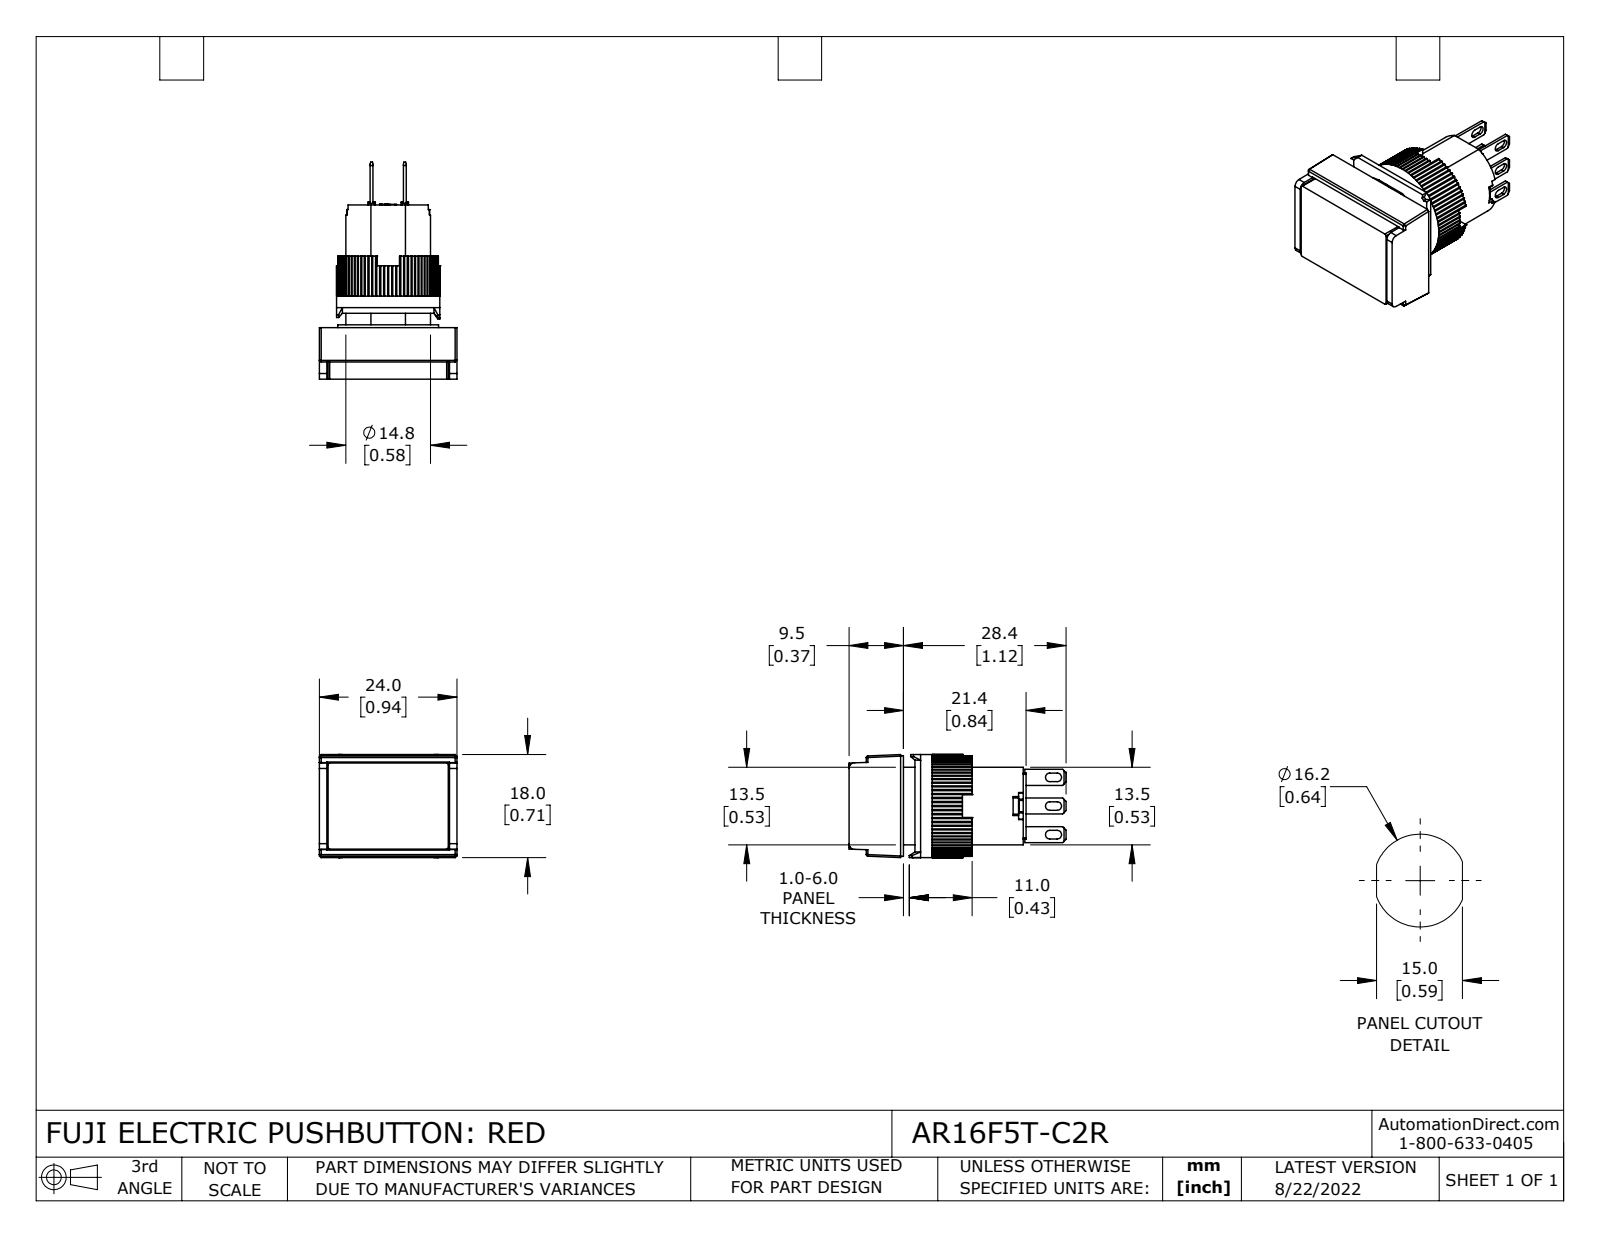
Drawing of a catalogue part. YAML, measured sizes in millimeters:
part_name: "AR16F5T-C2R"
step_written_by: "SolidWorks 2021 (CONFIG_CONTROL_DESIGN)"
units: millimeters
bodies: {solids: 12, faces: 813, planar: 632, cylindrical: 177, other: 4}
overall_size: [37.9, 24, 18]
volume: 7260
surface_area: 5886
round_holes:
  - {diameter: 13.8, count: 1}
  - {diameter: 14.8, count: 1}
round_bosses_or_shafts:
  - {diameter: 18, count: 1}
  - {diameter: 17.6, count: 1}
partial_cylinders:
  - {radius: 0.3, count: 80}
  - {radius: 0.2, count: 12}
  - {radius: 0.3, count: 6}
  - {radius: 0.8, count: 6}
  - {radius: 1, count: 2}
face_to_face_distances: [5.4, 9, 3.6, 12.5, 8.9, 3.5, 0.5, 21.4, 1.5, 11.5]
